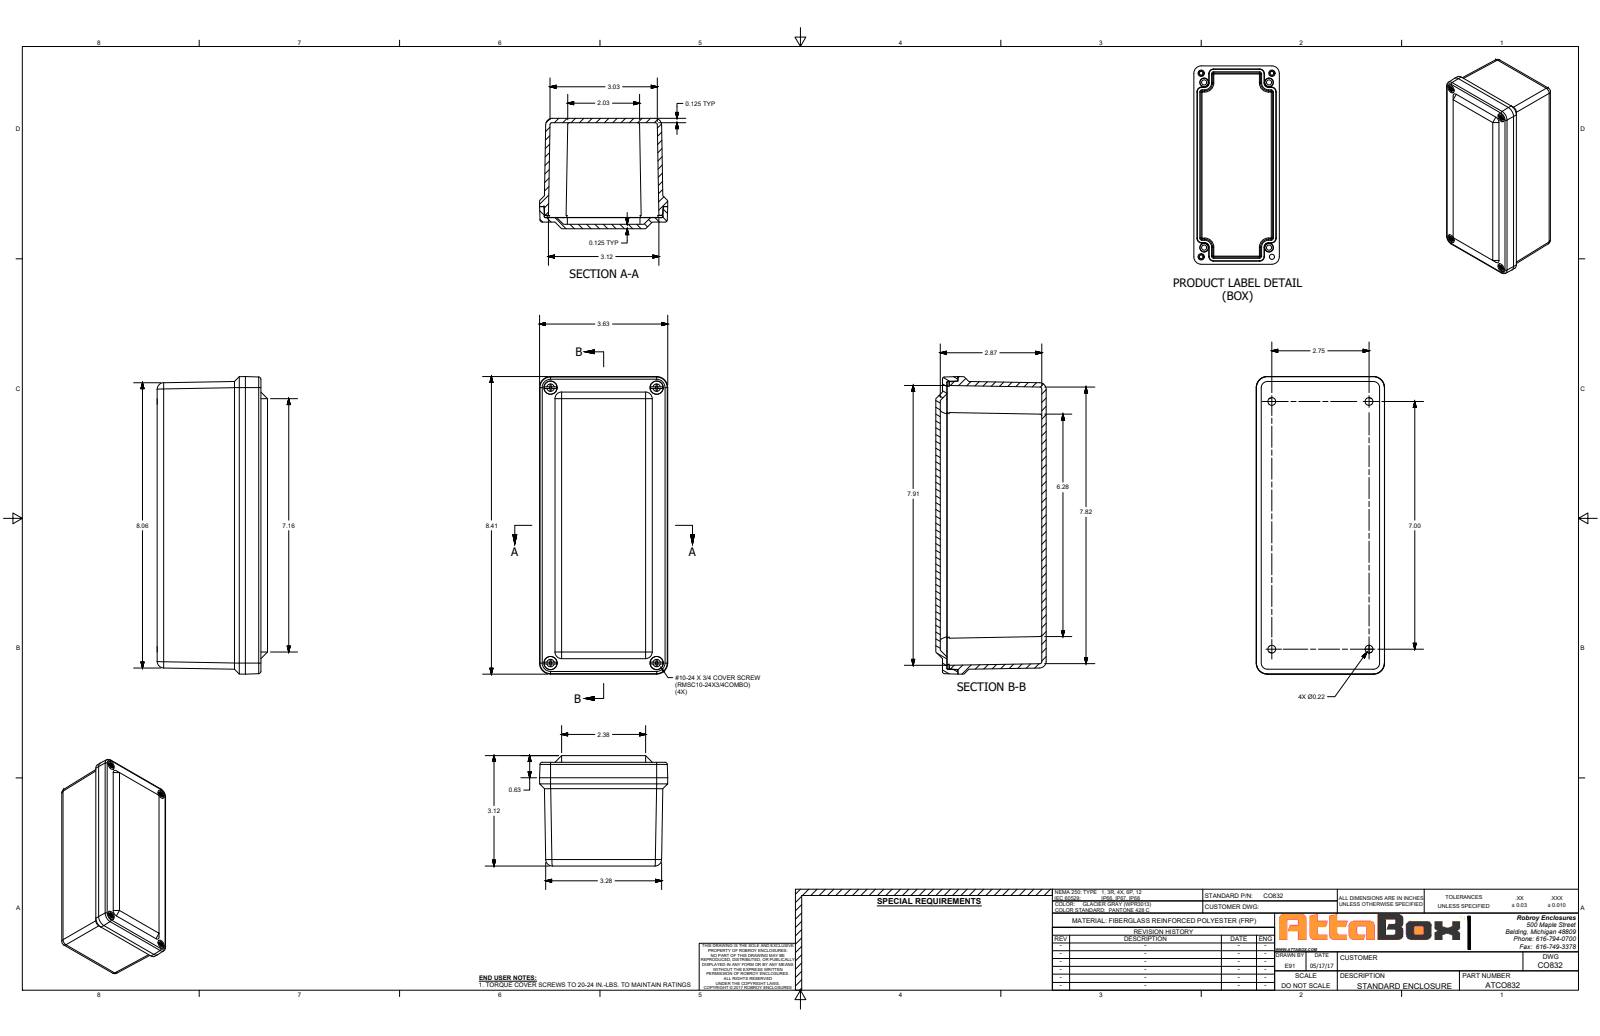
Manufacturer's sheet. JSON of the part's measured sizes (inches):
{"part_name": "CO832", "step_written_by": "SolidWorks 2018 (AUTOMOTIVE_DESIGN)", "units": "inches", "bodies": {"solids": 11, "faces": 375, "planar": 167, "cylindrical": 112, "other": 96}, "overall_size": [8.409, 3.625, 3.12], "volume_in3": 18.72, "surface_area_in2": 277.2, "round_holes": [[0.219, 8], [0.159, 4], [0.19, 4], [0.375, 4]], "round_bosses_or_shafts": [[0.371, 4], [0.27, 4], [0.177, 4]], "partial_cylinders_radius": [[0.031, 20], [0.012, 16], [0.048, 8], [0.176, 4], [0.22, 4], [0.313, 4], [0.325, 4], [0.188, 3]], "face_to_face_distances": [0.122, 0.125, 0.125, 3.12, 2.995, 2.995, 2.87, 0.187, 0.313, 0.5], "hole_center_spacings": [0.41, 2.901, 7.392, 7.93, 2.75, 3, 7, 7.52]}
